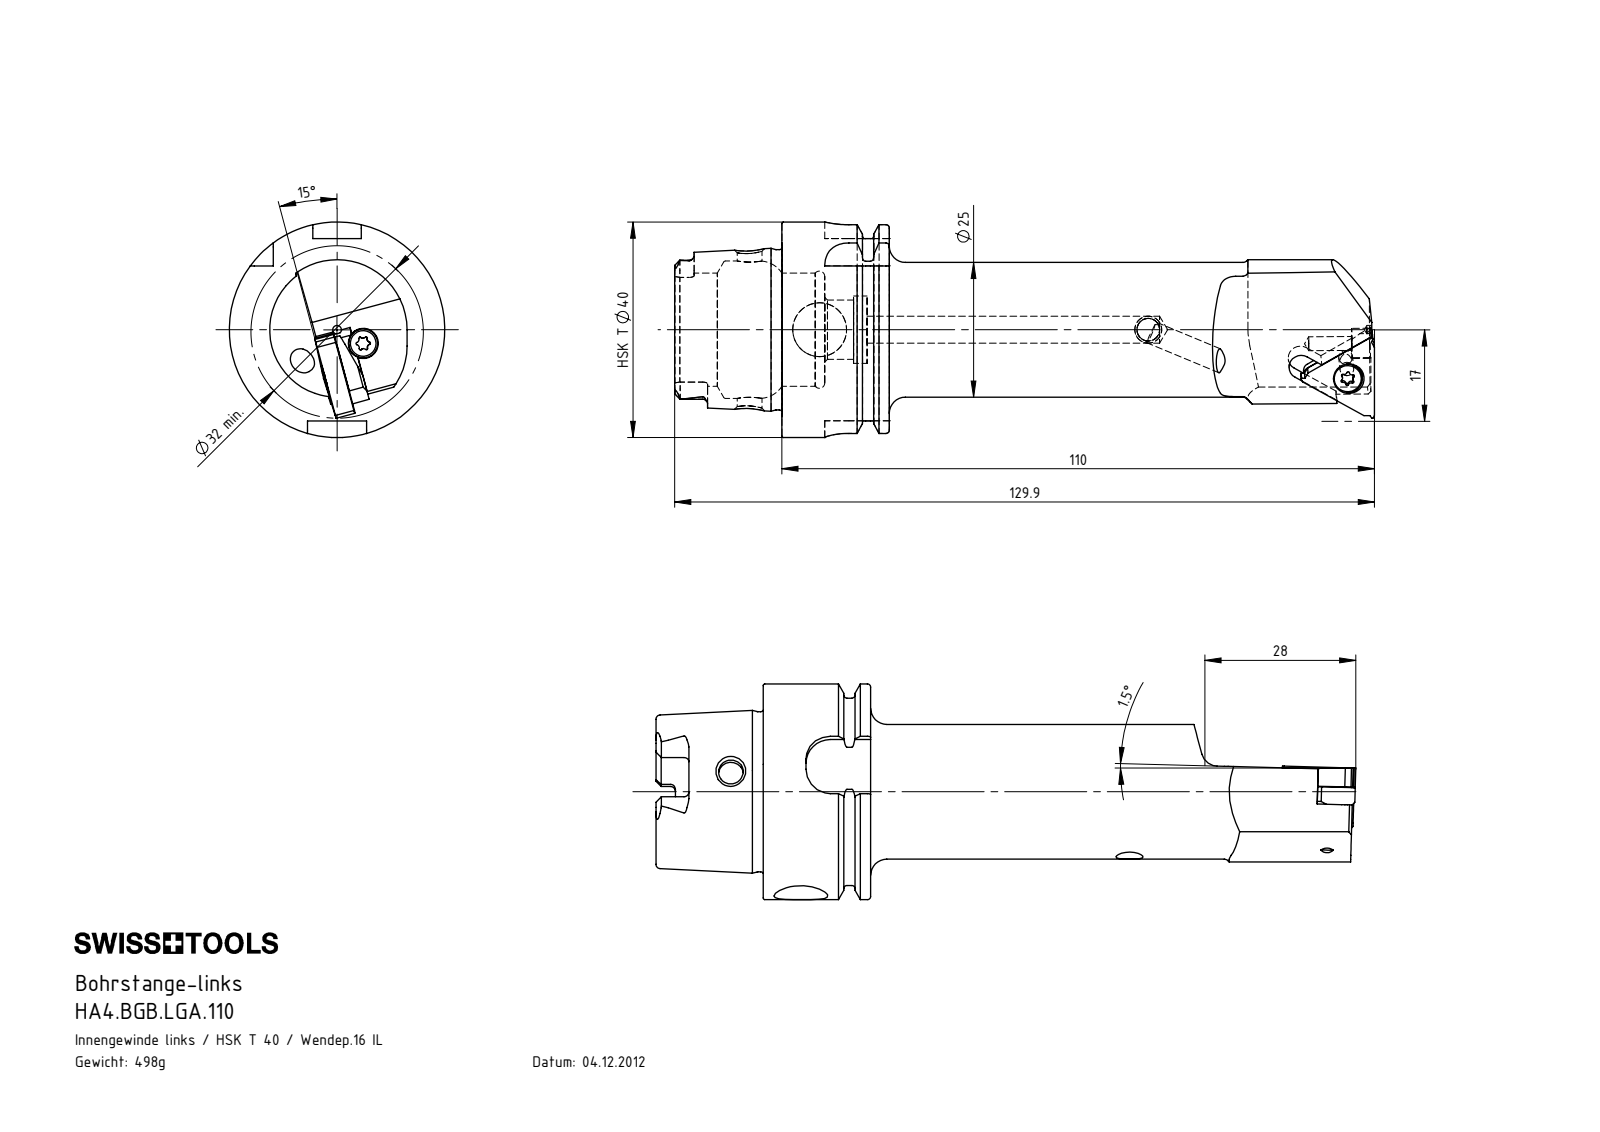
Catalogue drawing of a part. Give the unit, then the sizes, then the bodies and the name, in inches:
Units: inches
Overall size (bounding box): 5.114 × 1.575 × 1.575
Round holes (diameter × count): ⌀0.102 ×2, ⌀0.165 ×2, ⌀0.197 ×2, ⌀0.063 ×1, ⌀0.157 ×1, ⌀0.158 ×1, ⌀0.181 ×1, ⌀0.394 ×1, ⌀0.433 ×1, ⌀0.492 ×1, ⌀0.827 ×1, ⌀1.004 ×1
Round bosses / shafts (diameter × count): ⌀0.125 ×2, ⌀1.575 ×1, ⌀1.368 ×1, ⌀1.17 ×1, ⌀0.984 ×1, ⌀0.217 ×1, ⌀0.213 ×1, ⌀0.109 ×1
Partial cylindrical surfaces — rounded edges, fillets, slot ends (radius × count): R0.009 ×12, R0.022 ×12, R0.035 ×6, R0.074 ×4, R0.177 ×4, R0.004 ×2, R0.512 ×2, R0.01 ×1
Main face-to-face distances: 0.785, 0.472, 0.313, 0.262, 0.136, 0.126, 0.783, 1.096, 1.569, 0.27
Hole centre spacings: 2.402, 18.421, 18.422
Volume: 3.852 in³ · Surface area: 29.09 in²
Bodies: 5 solids, 324 faces (111 planar, 114 cylindrical, 99 other)
Part name (STEP PRODUCT): HA4-BGB.LGA.110; WGB-ER3.001.007_A; LT16ER; WGB-ER2.102.003_A (+2 more)
STEP written by: SolidWorks 2012 (AUTOMOTIVE_DESIGN)
